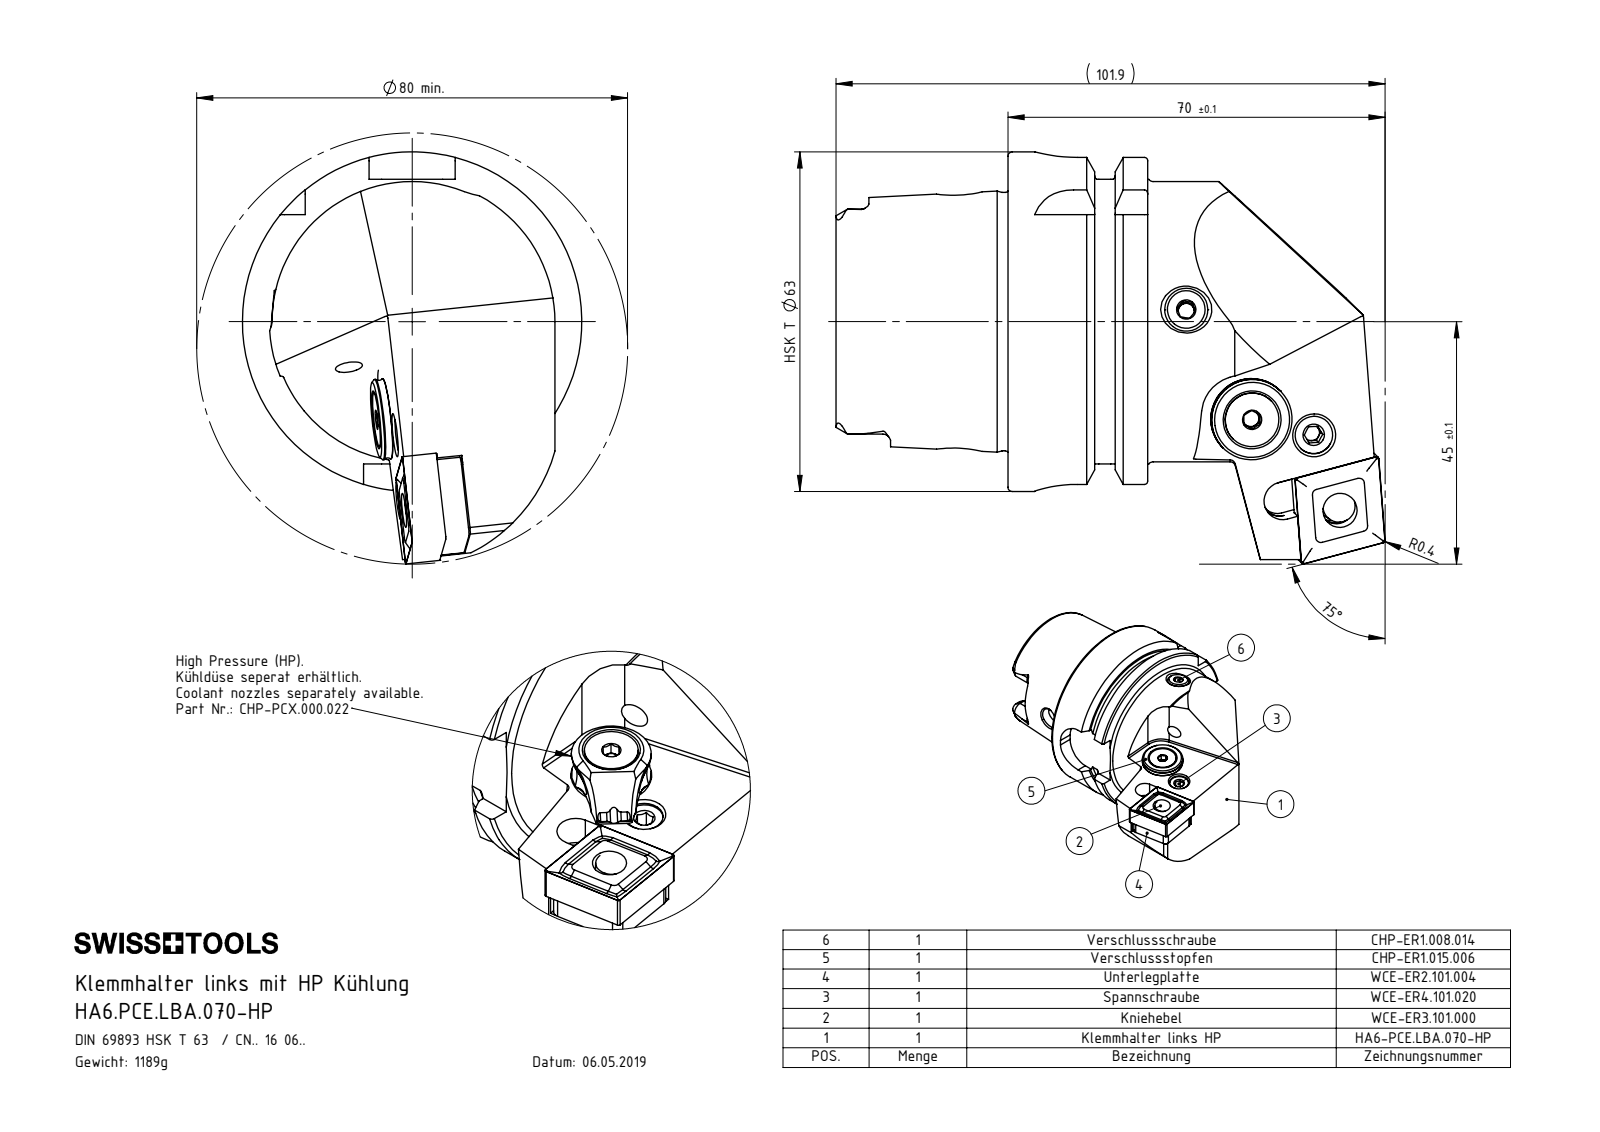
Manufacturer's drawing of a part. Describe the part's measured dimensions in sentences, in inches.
The part is named "HA6-PCE.LBA.070-HP; WCE-ER1.101.000; CHP-ER1.008.014_A; ISO 8752 2x8 (+8 more)". Its 3-D file was written by "SolidWorks 2017 (CONFIG_CONTROL_DESIGN)". It is 12 solids with 607 faces: 176 planar, 172 cylindrical and 259 other. Overall it measures 4.012 by 3.01 by 2.48 inches. Its volume is 9.196 cubic inches and its surface area 58.47 square inches. Round holes: 2 of diameter 0.165, 2 of diameter 0.197, 2 of diameter 0.276, 2 of diameter 0.331, 1 of diameter 0.047, 1 of diameter 0.079, 1 of diameter 0.118, 1 of diameter 0.209, 1 of diameter 0.25, 1 of diameter 0.295, 1 of diameter 0.317, 1 of diameter 0.394. Round bosses or shafts: 2 of diameter 0.315, 1 of diameter 2.48, 1 of diameter 2.163, 1 of diameter 2.047, 1 of diameter 1.887, 1 of diameter 0.585, 1 of diameter 0.528, 1 of diameter 0.394. Partial cylindrical surfaces (rounded edges, fillets, slot ends): 7 of radius 0.039, 6 of radius 0.055, 5 of radius 0.138, 4 of radius 0.016, 4 of radius 0.02, 4 of radius 0.059, 4 of radius 0.113, 4 of radius 0.315. The main face-to-face distances are 1.022, 0.63, 0.392, 0.238, 1.256, 1.648, 2.278, 2.079, 0.594, 0.858. The hole center spacings are 0.178, 0.442, 0.805, 0.813, 0.481, 0.583, 0.59, 0.942.
